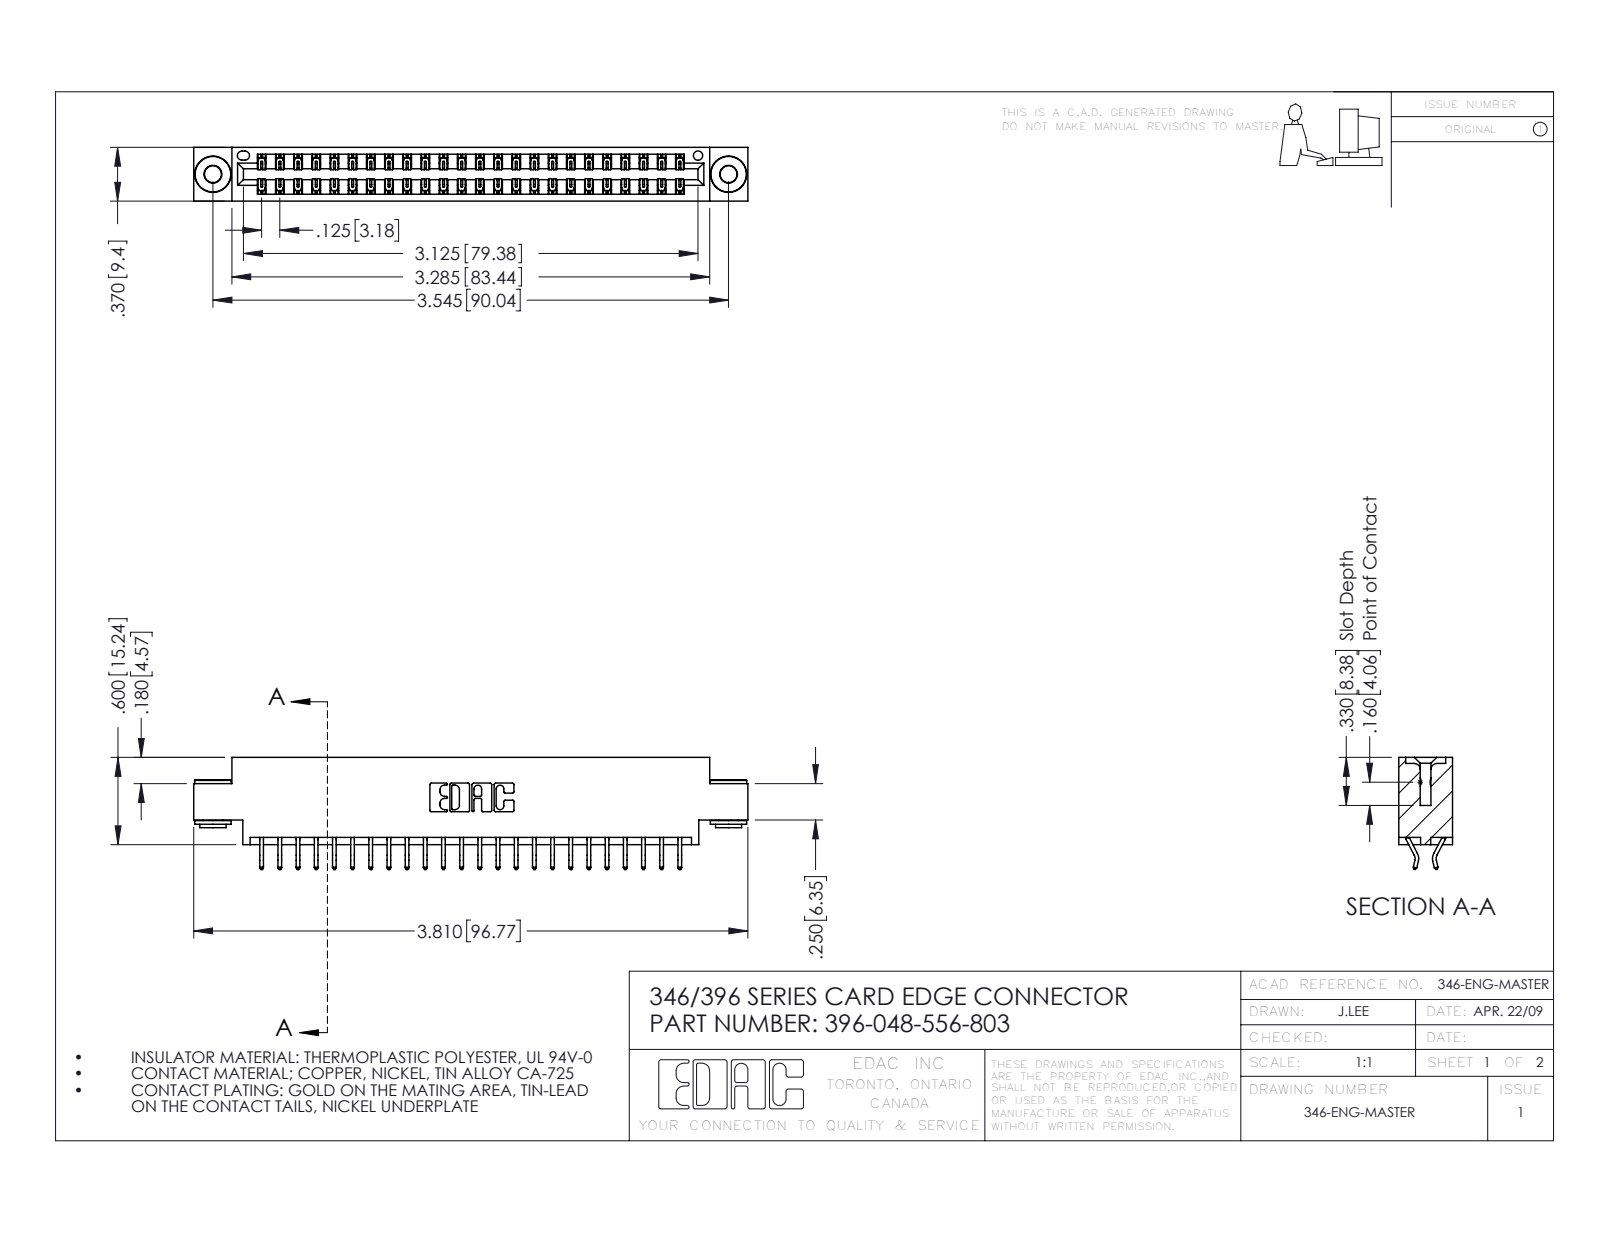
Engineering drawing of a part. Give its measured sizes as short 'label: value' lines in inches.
name: 345-292-001_556 Tail; 396-048-556-803; 345-250-002_345-250-002-102; 346 Part_0.170 Offset - 0.156 Dia-TH
written by: SolidWorks 2016 (CONFIG_CONTROL_DESIGN)
unit: in
bodies: 51 solids, 2948 faces (1962 planar, 978 cylindrical, 8 other)
size: 3.81 × 0.77 × 0.37
volume: 0.559 in³; area: 19.62 in²
holes: 2× ⌀0.116, 2× ⌀0.156, 1× ⌀0.064
bosses: 2× ⌀0.25, 2× ⌀0.18, 2× ⌀0.136
rounds: 72× R0.006, 22× R0.01, 6× R0.007, 6× R0.031, 3× R0.026, 2× R0.01, 2× R0.014, 2× R0.022
face distances: 0.048, 0.322, 0.37, 0.25, 0.025, 0.275, 0.072, 0.298, 0.148, 0.222
hole spacings: 0.246, 3.337, 3.545
